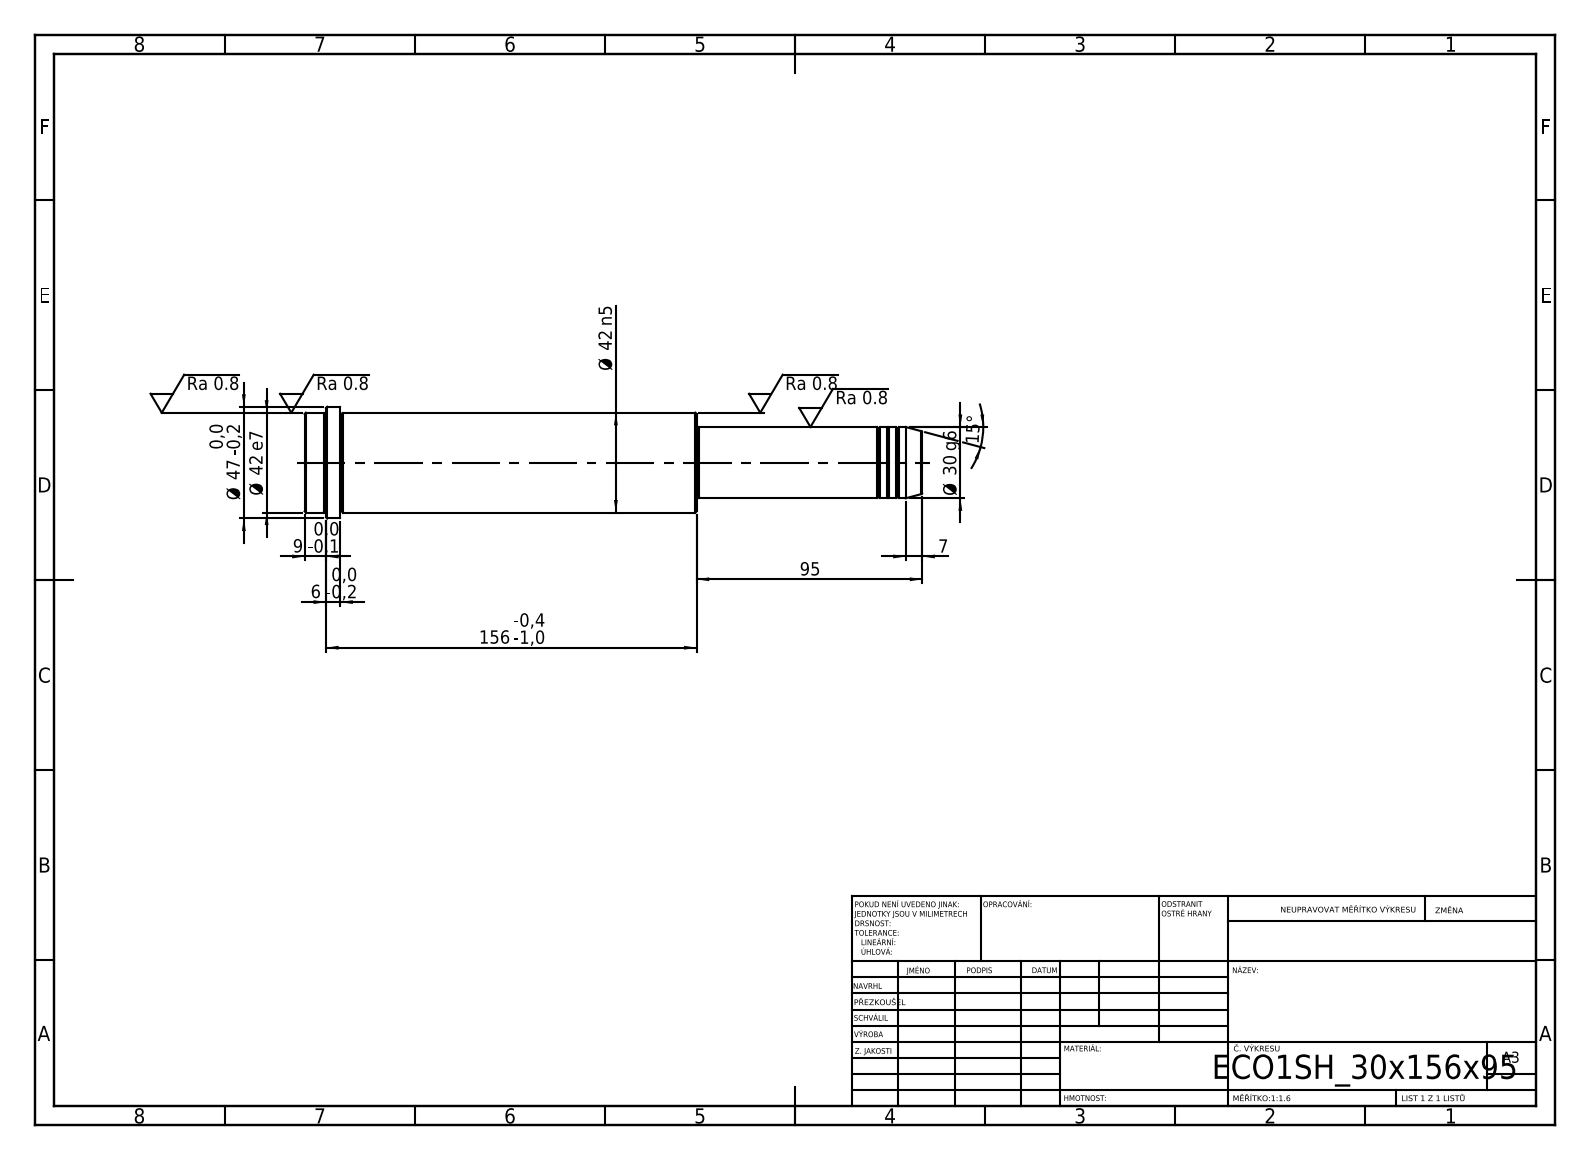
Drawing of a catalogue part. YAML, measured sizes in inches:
step_written_by: "SolidWorks 2019 (CONFIG_CONTROL_DESIGN)"
units: inches
bodies: {solids: 1, faces: 52, planar: 6, cylindrical: 16, other: 30}
overall_size: [10.236, 1.85, 1.85]
volume: 18.12
surface_area: 53.26
round_bosses_or_shafts:
  - {diameter: 1.85, count: 1}
  - {diameter: 1.654, count: 1}
  - {diameter: 1.181, count: 1}
  - {diameter: 1.142, count: 1}
face_to_face_distances: [6.496, 3.74, 10.236, 9.646, 5.906, 0.591, 9.882, 6.142, 0.236, 0.354]
